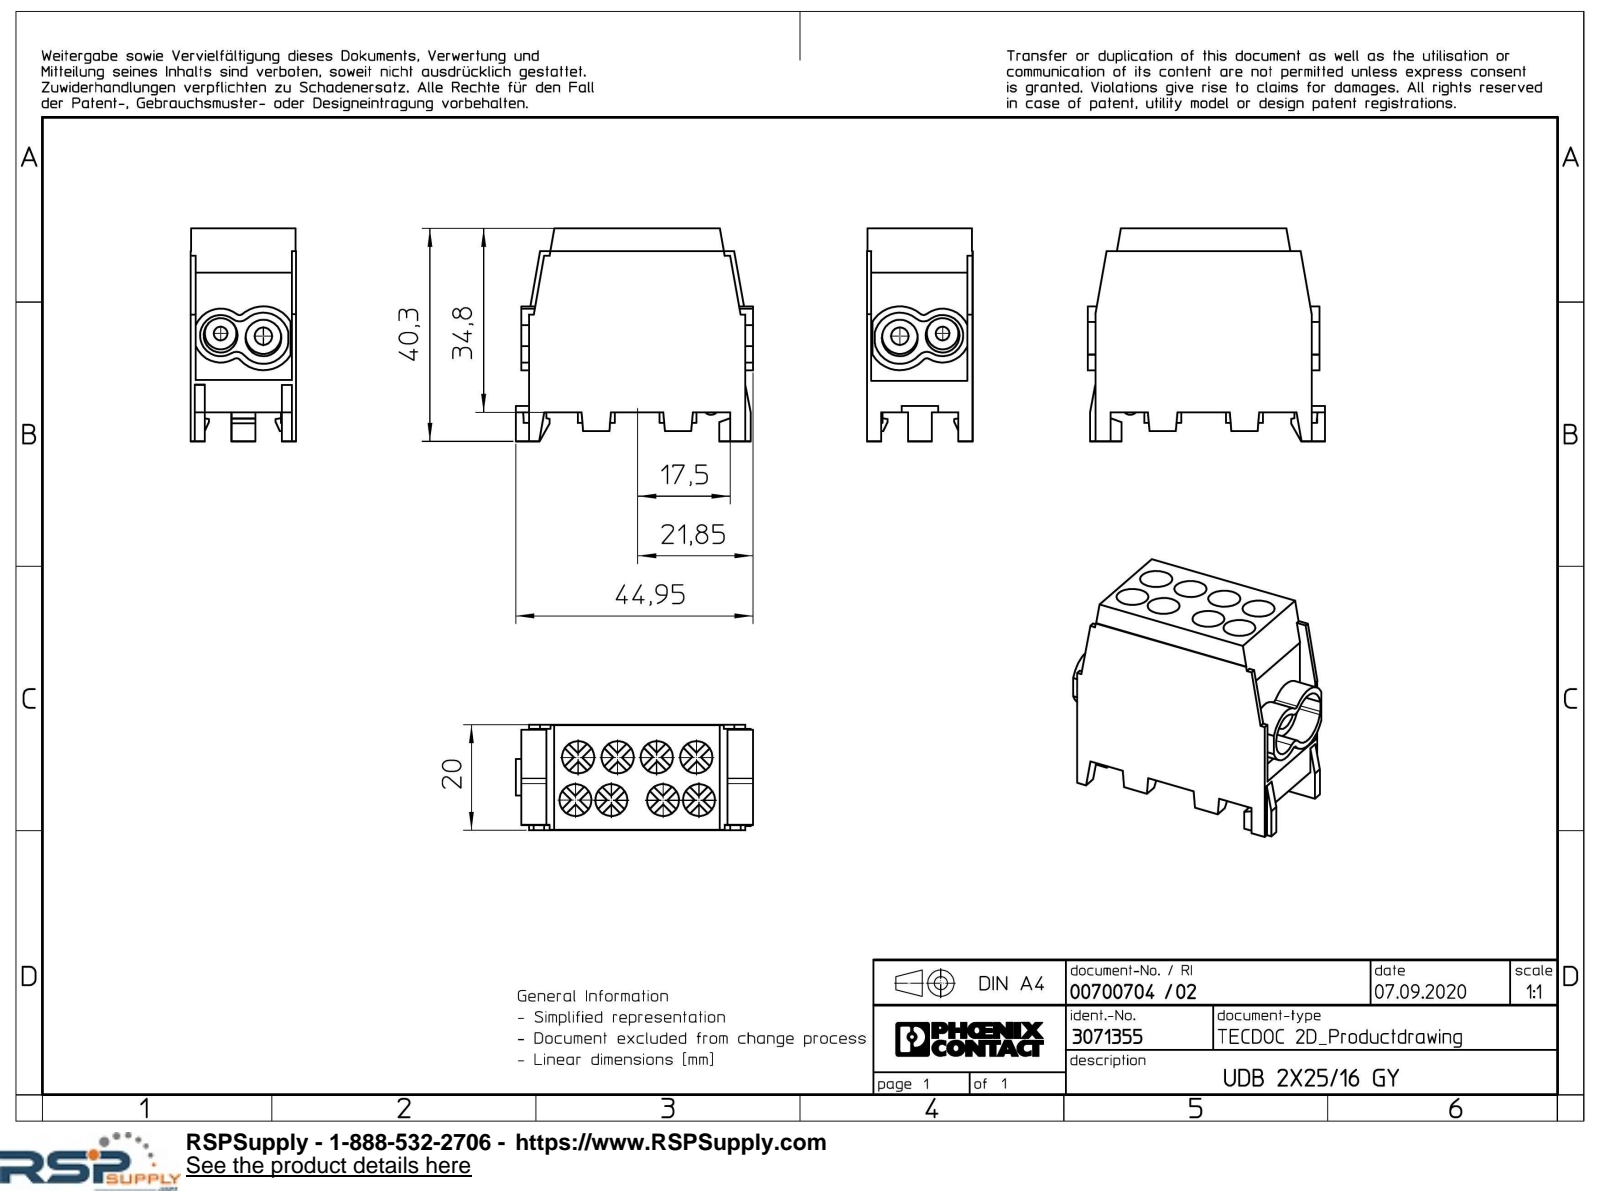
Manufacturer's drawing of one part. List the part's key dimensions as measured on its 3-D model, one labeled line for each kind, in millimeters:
Part name (STEP PRODUCT): UDB_2x25_16_GY-select
STEP written by: Creo Elements/Direct Modeling 20.1A 29-Sep-2018 (C) Parametric Technology GmbH (AUTOMOTIVE_DESIGN)
Units: millimetres
Bodies: 1 solid, 309 faces (242 planar, 59 cylindrical, 8 other)
Overall size (bounding box): 44.95 × 40.3 × 20
Volume: 22 415 mm³ · Surface area: 9 855 mm²
Round holes (diameter × count): ⌀6.05 ×4, ⌀6.1 ×4, ⌀6 ×1, ⌀6.7 ×1
Partial cylindrical surfaces — rounded edges, fillets, slot ends (radius × count): R0.8 ×3, R2 ×3, R3.4 ×2, R1.5 ×1, R3.2 ×1, R3.2 ×1, R3.9 ×1, R4.85 ×1
Main face-to-face distances: 20, 34.8, 3.35, 37.65, 19.9, 34.3, 1, 0.9, 0.8, 0.7
Hole centre spacings: 6.8, 7.5, 8.12, 8.19, 10.26, 11.38, 11.81, 14.9
